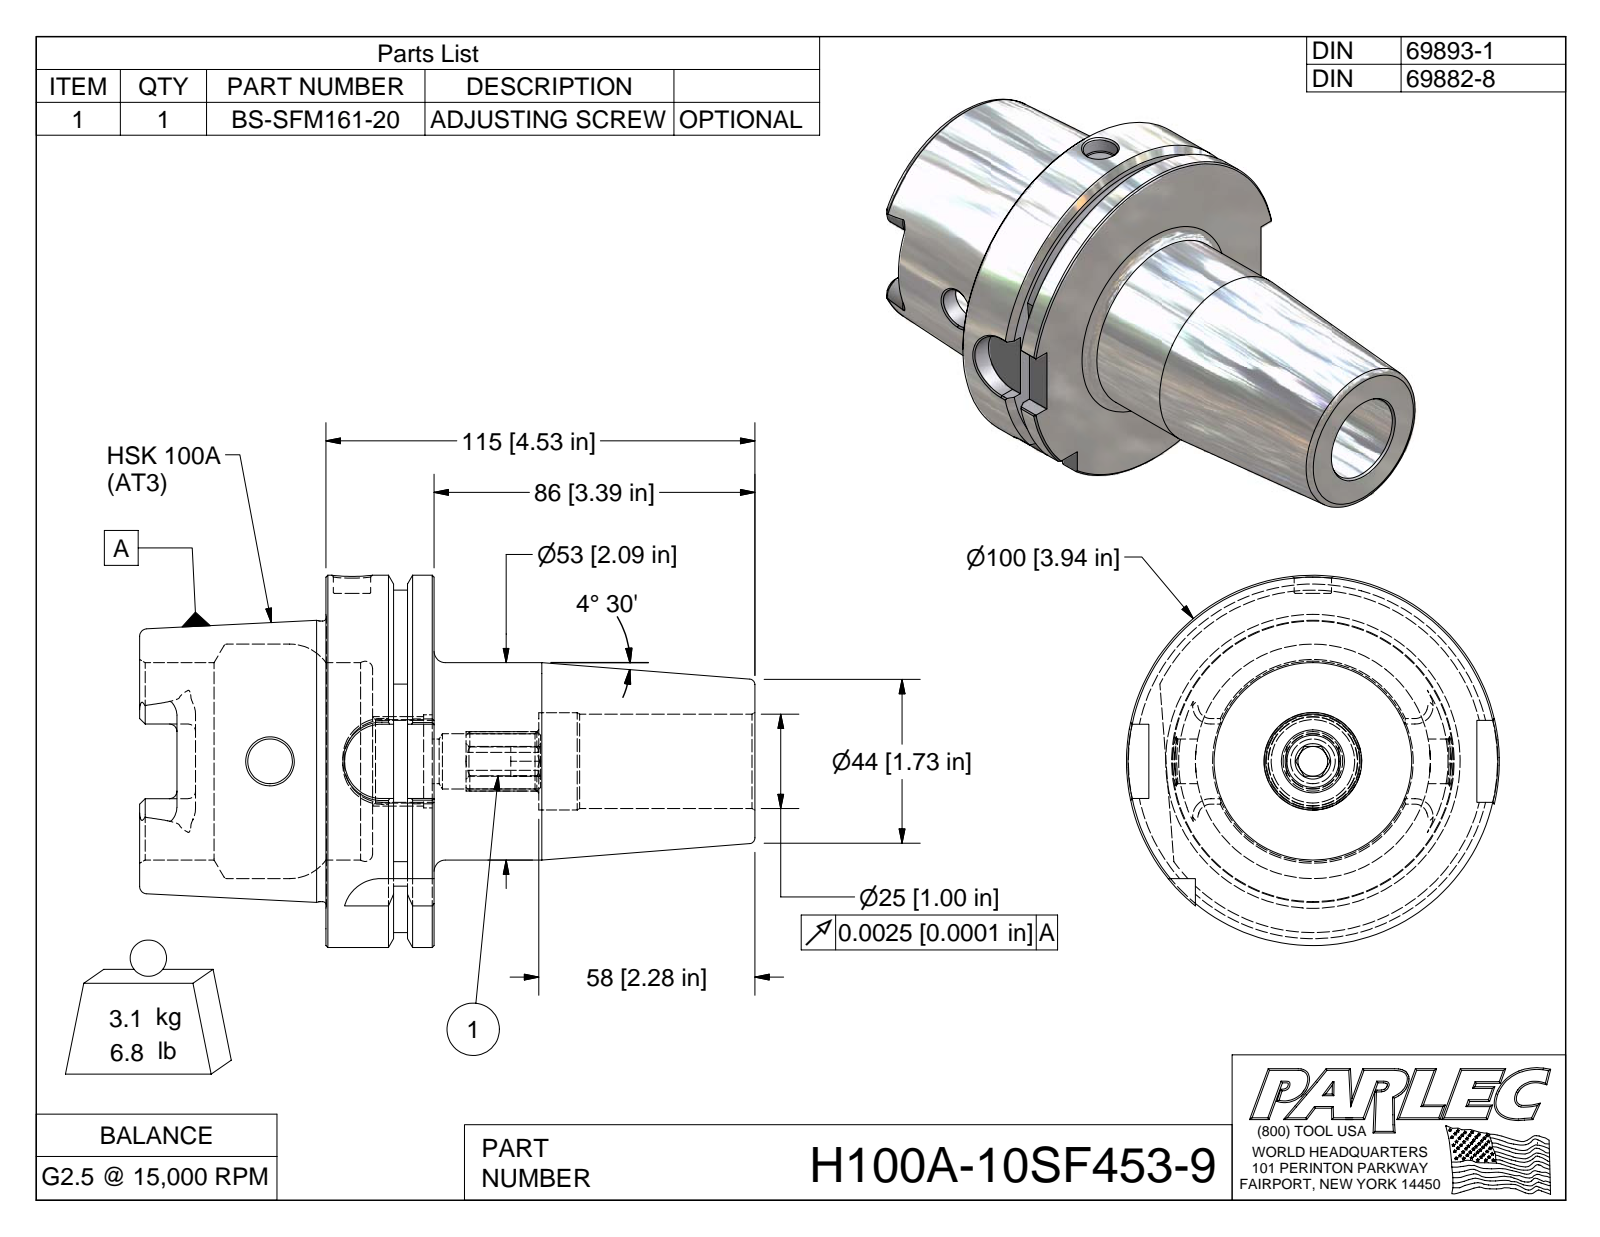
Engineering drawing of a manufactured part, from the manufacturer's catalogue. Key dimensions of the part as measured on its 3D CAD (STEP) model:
Part name (STEP PRODUCT): H100A-10SF453-9; H100A-10SF453-9-1; BS-SFM161-20
STEP written by: Autodesk Inventor 2009 (AUTOMOTIVE_DESIGN)
Units: inches
Bodies: 2 solids, 149 faces (49 planar, 30 cylindrical, 70 other)
Overall size (bounding box): 6.499 × 3.937 × 3.937
Volume: 23.92 in³ · Surface area: 108.6 in²
Round holes (diameter × count): ⌀0.394 ×1, ⌀0.472 ×1, ⌀0.881 ×1, ⌀0.985 ×1, ⌀0.999 ×1, ⌀1.029 ×1, ⌀2.087 ×1, ⌀2.48 ×1
Round bosses / shafts (diameter × count): ⌀3.937 ×1, ⌀2.967 ×1
Partial cylindrical surfaces — rounded edges, fillets, slot ends (radius × count): R0.394 ×4, R0.079 ×3, R0.192 ×2, R0.315 ×1, R1.811 ×1
Main face-to-face distances: 1.142, 0.492, 0.65, 1.969, 2.461, 3.11, 6.498, 4.53, 4.038, 3.388
